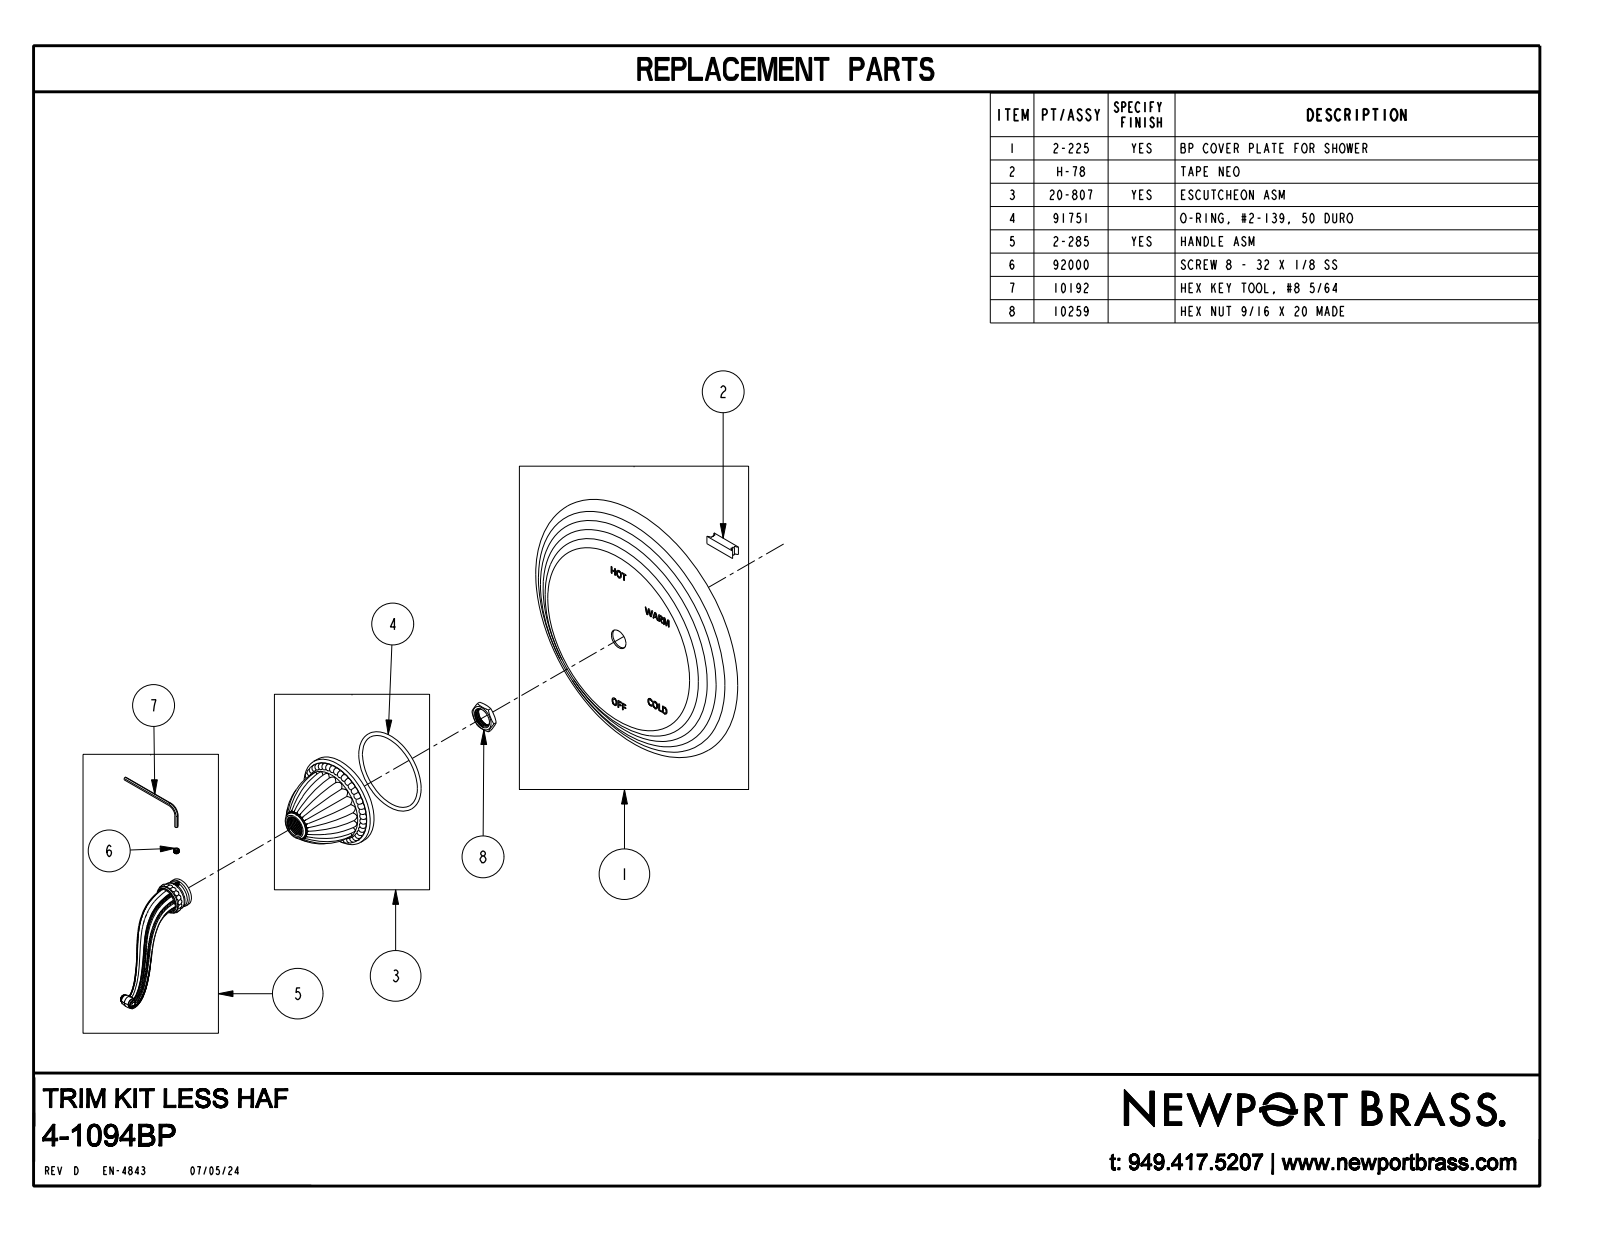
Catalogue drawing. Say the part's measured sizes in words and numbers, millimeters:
The part is named "4-1094BP". Its 3-D file was written by "CREO PARAMETRIC BY PTC INC, 2018400 (CONFIG_CONTROL_DESIGN)". It is 1 solid with 3321 faces: 452 planar, 1100 cylindrical and 1769 other. Overall it measures 196.9 by 196.9 by 122.1 millimeters. Its volume is 541 900 cubic millimeters and its surface area 78 840 square millimeters. Round holes: 189 of diameter 1, 49 of diameter 1.3, 23 of diameter 1.1, 11 of diameter 1. Round bosses or shafts: 1 of diameter 65.3, 1 of diameter 20.1, 1 of diameter 19.7, 1 of diameter 10.2. The main face-to-face distances are 19.2, 65.9, 46.7, 19.1, 46.8, 65.1, 46.1, 46, 0.8, 24.2. The hole center spacings are 4.9, 5.5, 6.7, 8.5, 9.2, 13, 1.4, 1.4.
